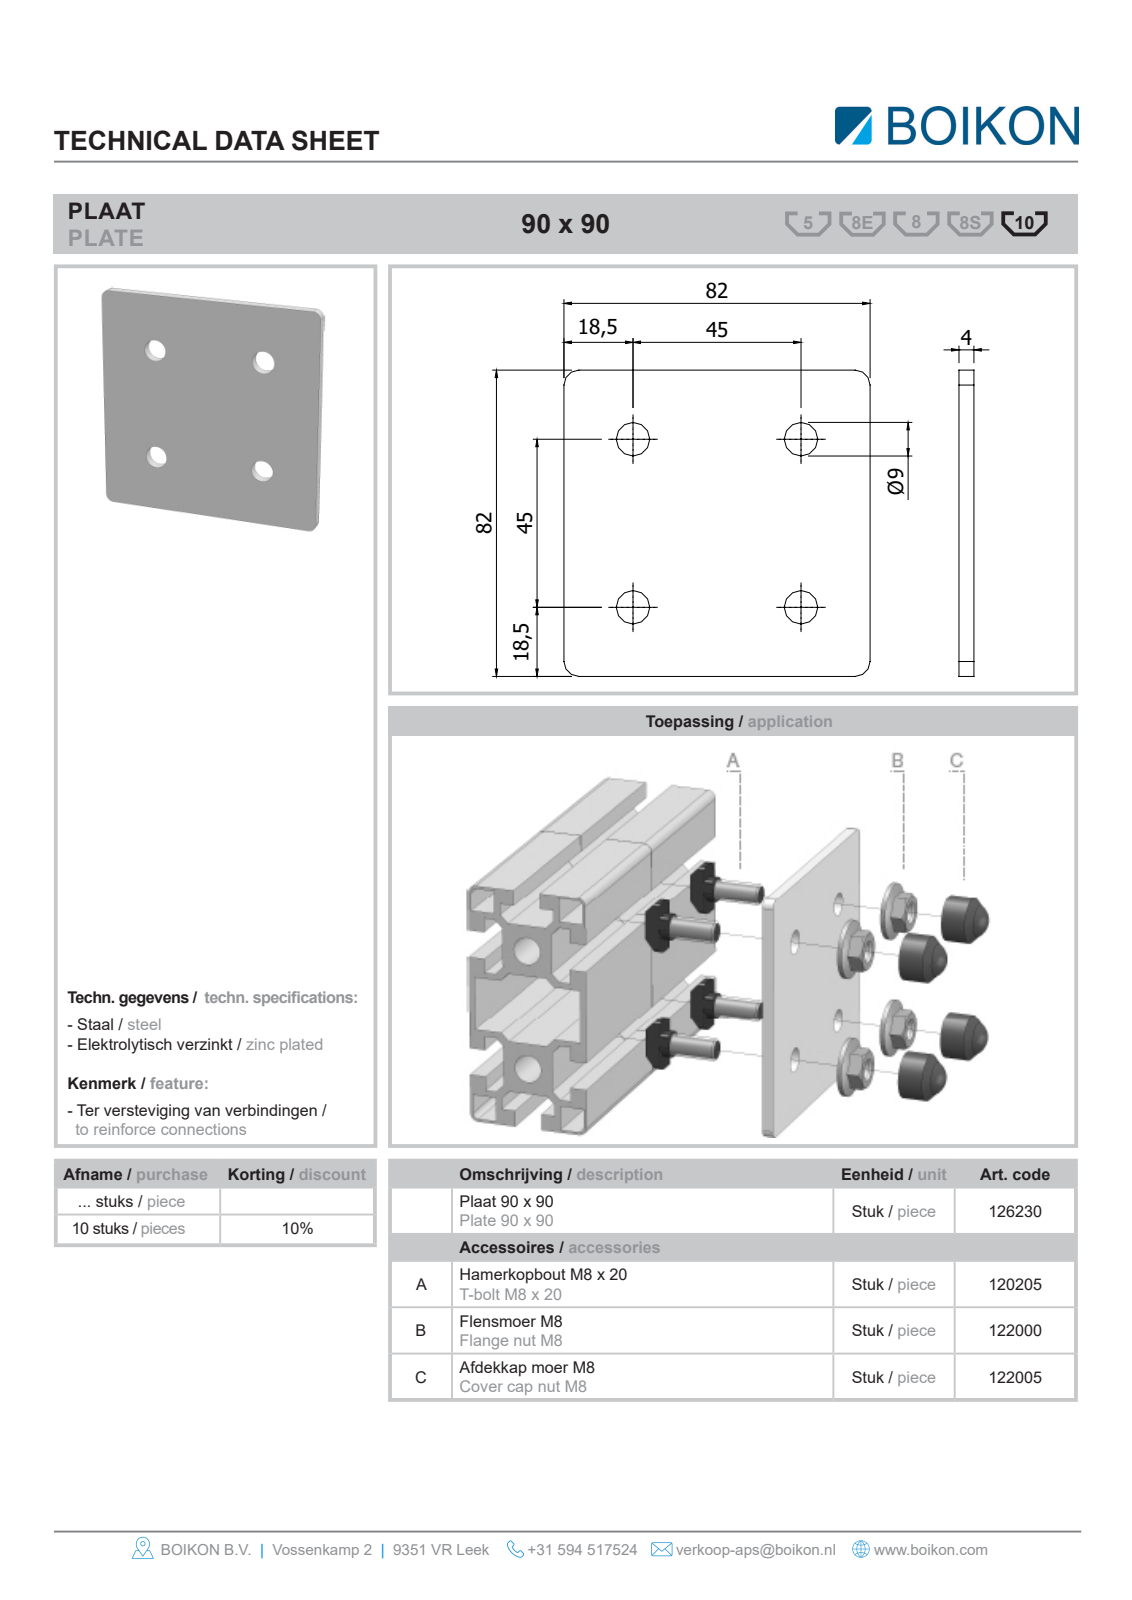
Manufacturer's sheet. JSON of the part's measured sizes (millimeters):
{"part_name": "Root; 126230Plaat 90 x 90BOIKON; 122000Flensmoer M8BOIKON; 122005Afdekkap voor moer M8BOIKON (+1 more)", "step_written_by": "HiCAD 2013 1802.4 Build 509 (AUTOMOTIVE_DESIGN)", "units": "millimeters", "bodies": {"solids": 13, "faces": 366, "planar": 250, "cylindrical": 64, "other": 52}, "overall_size": [90, 90, 33.3], "volume_mm3": 50870, "surface_area_mm2": 31270, "round_holes": [[8, 4], [9, 4]], "round_bosses_or_shafts": [[21, 4], [16.8, 4], [6.47, 4]], "partial_cylinders_radius": [[1, 20], [5, 8], [1.16, 4], [3, 4], [9.5, 4]], "face_to_face_distances": [4, 13, 7, 45, 90, 11, 38.97, 22.5, 9.5, 11.8], "hole_center_spacings": [45, 63.64]}
